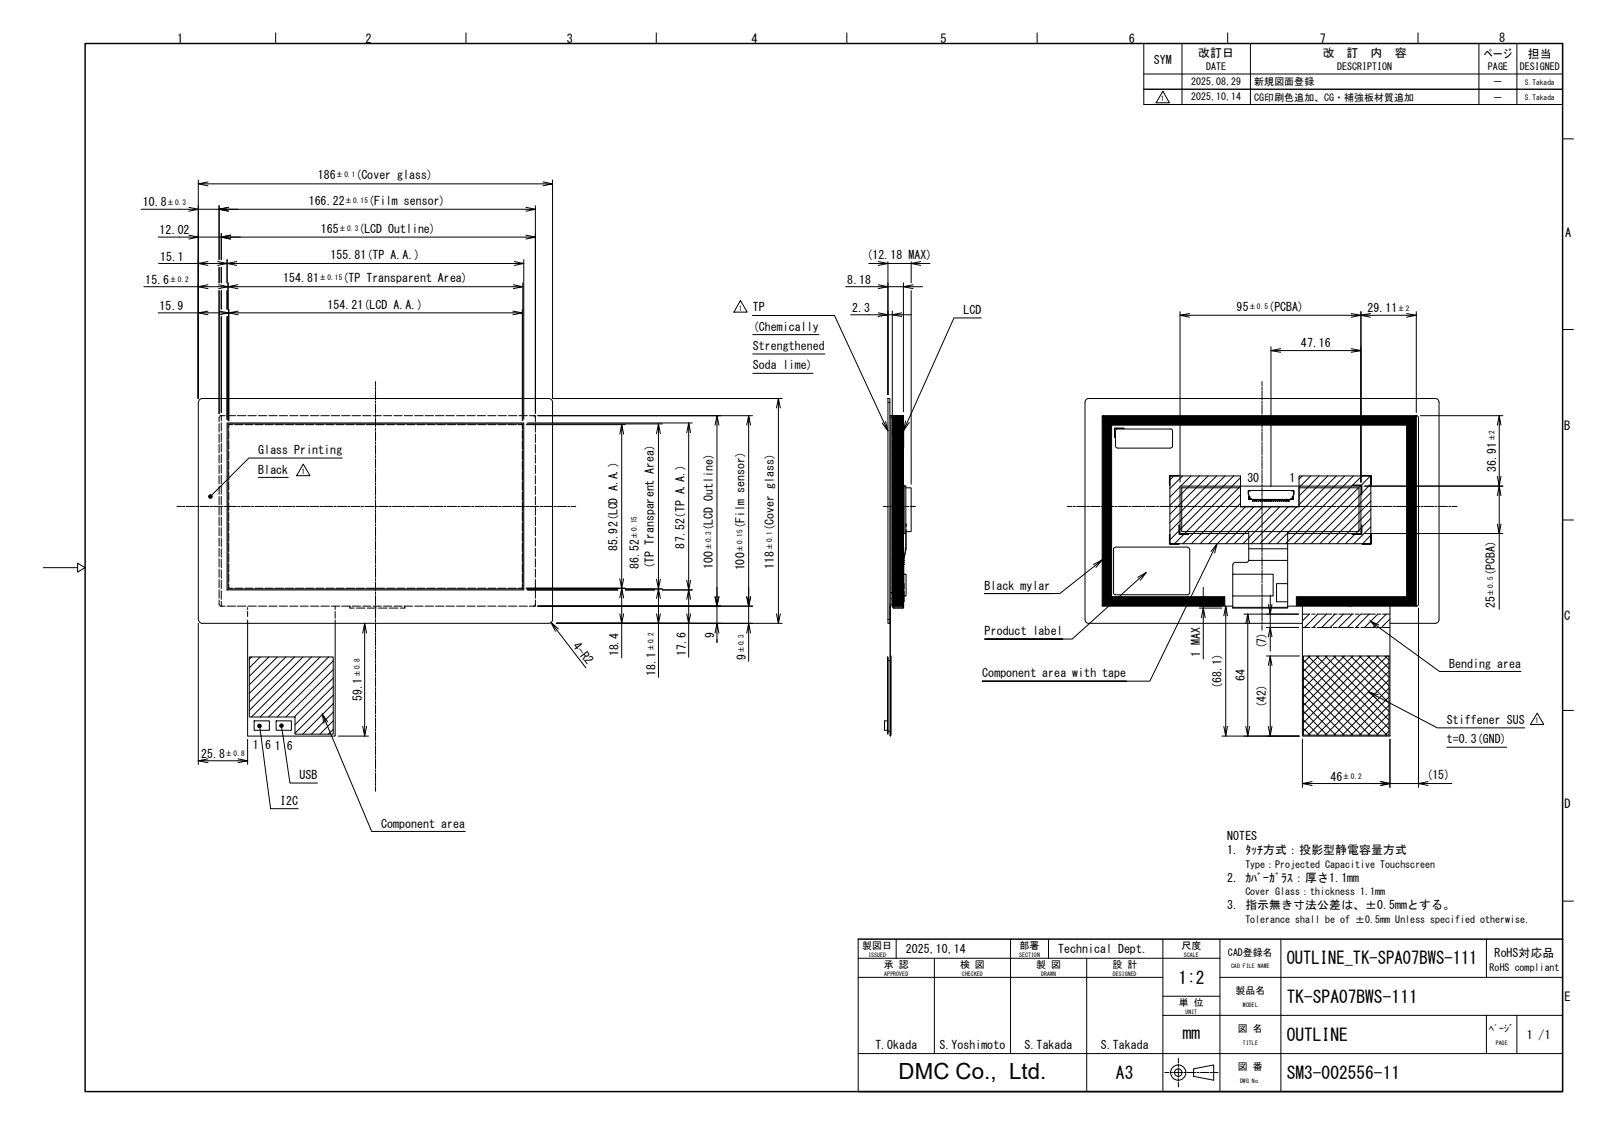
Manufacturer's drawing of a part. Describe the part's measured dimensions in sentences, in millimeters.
The part is named "HP_TK-SPA07BWS-111". Its 3-D file was written by "Autodesk Inventor 2024 (AUTOMOTIVE_DESIGN)". It is 1 solid with 1138 faces: 919 planar, 219 cylindrical and 0 other. Overall it measures 186 by 177.1 by 13.88 millimeters. Its volume is 139 884 cubic millimeters and its surface area 89 876 square millimeters. Partial cylindrical surfaces (rounded edges, fillets, slot ends): 95 of radius 0.1, 14 of radius 1, 4 of radius 0.3, 4 of radius 0.33, 4 of radius 2, 2 of radius 0.15, 2 of radius 0.2, 2 of radius 0.42. The main face-to-face distances are 1.5, 0.8, 2.3, 8.13, 5.83, 6.63, 1.2, 1.1, 7.03, 8.18.
